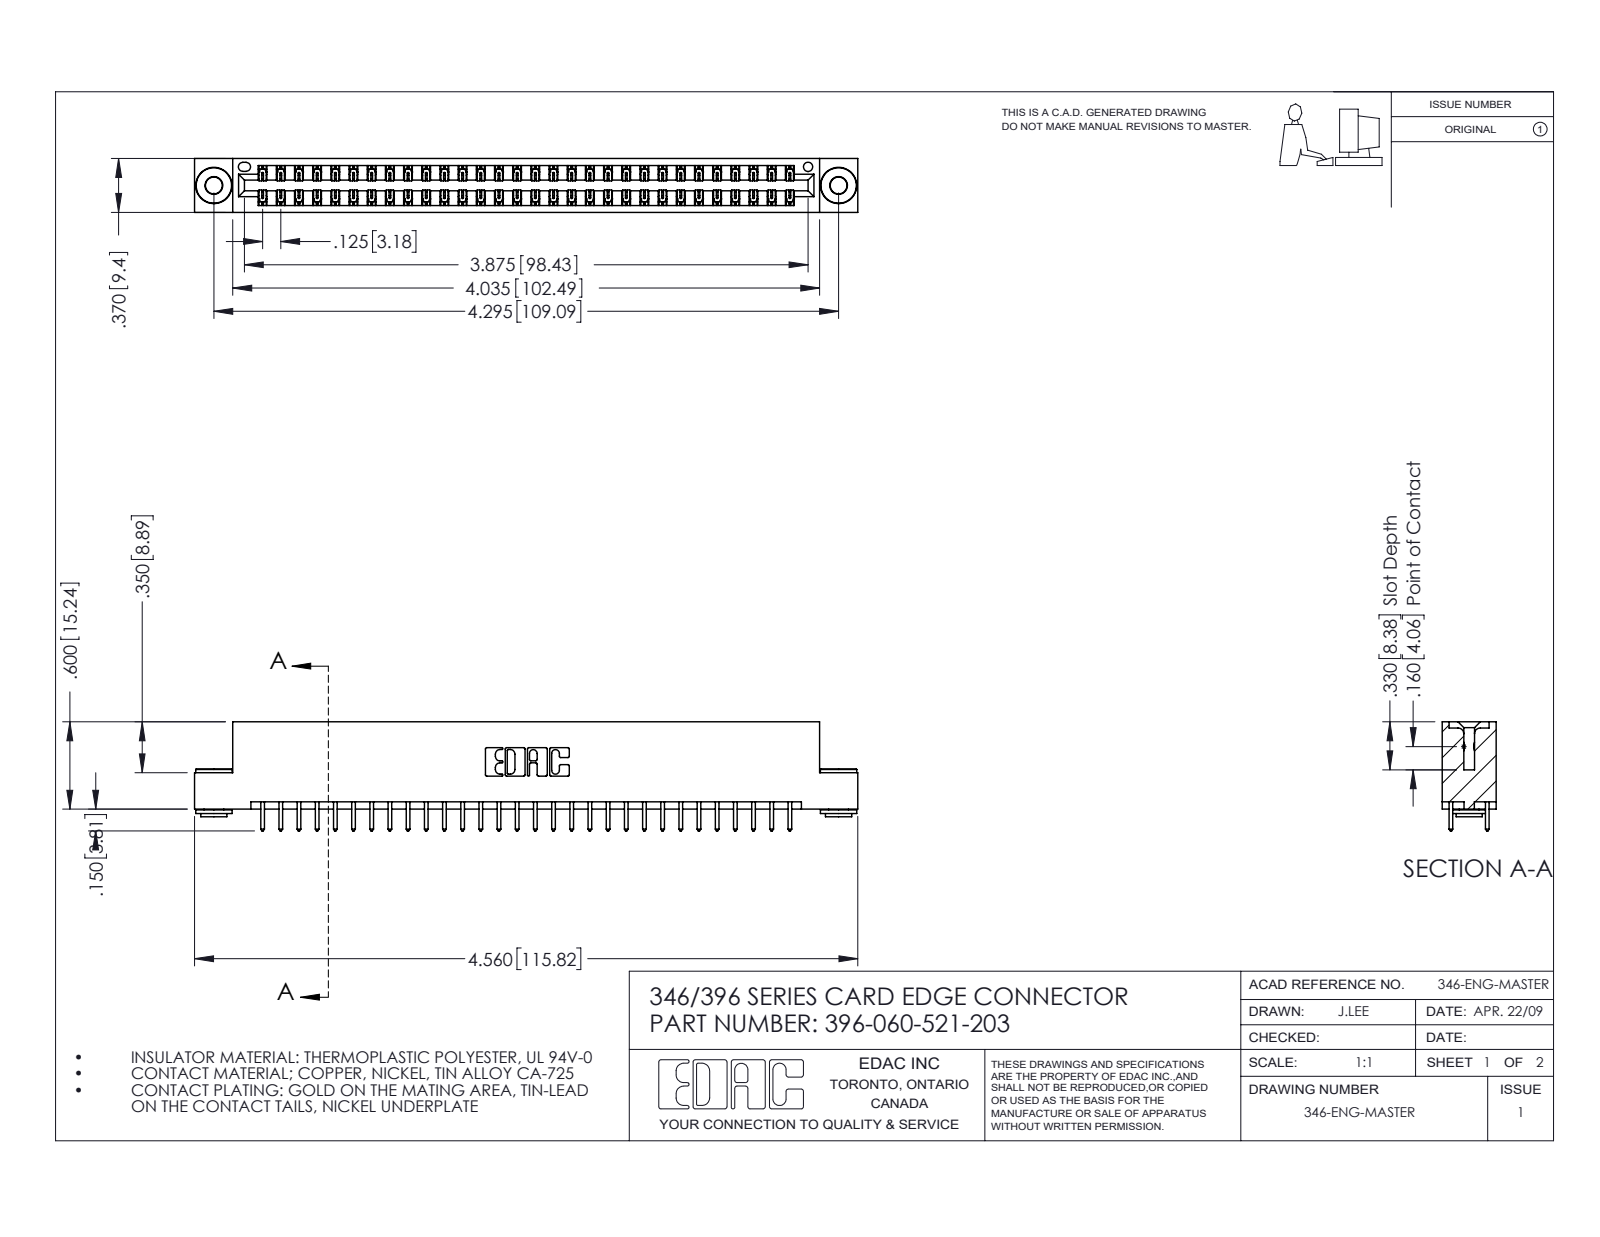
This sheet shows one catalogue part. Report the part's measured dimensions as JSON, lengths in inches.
{"part_name": "345-250-002_345-250-002-102; 346 Part_Flush Mounting Lugs - 0.156 Dia-TH; 345-292-001_345-293-121; 396-060-521-203", "step_written_by": "SolidWorks 2016 (CONFIG_CONTROL_DESIGN)", "units": "inches", "bodies": {"solids": 63, "faces": 3280, "planar": 2186, "cylindrical": 1086, "other": 8}, "overall_size": [4.56, 0.75, 0.37], "volume_in3": 0.683, "surface_area_in2": 23.64, "round_holes": [[0.116, 2], [0.156, 2], [0.064, 1]], "round_bosses_or_shafts": [[0.25, 2], [0.18, 2], [0.136, 2]], "partial_cylinders_radius": [[0.006, 90], [0.01, 60], [0.01, 22], [0.007, 6], [0.031, 6], [0.026, 3], [0.014, 2], [0.022, 2]], "face_to_face_distances": [0.048, 0.322, 0.25, 0.37, 0.025, 0.072, 0.298, 0.275, 0.148, 0.222], "hole_center_spacings": [0.246, 4.087, 4.295]}
